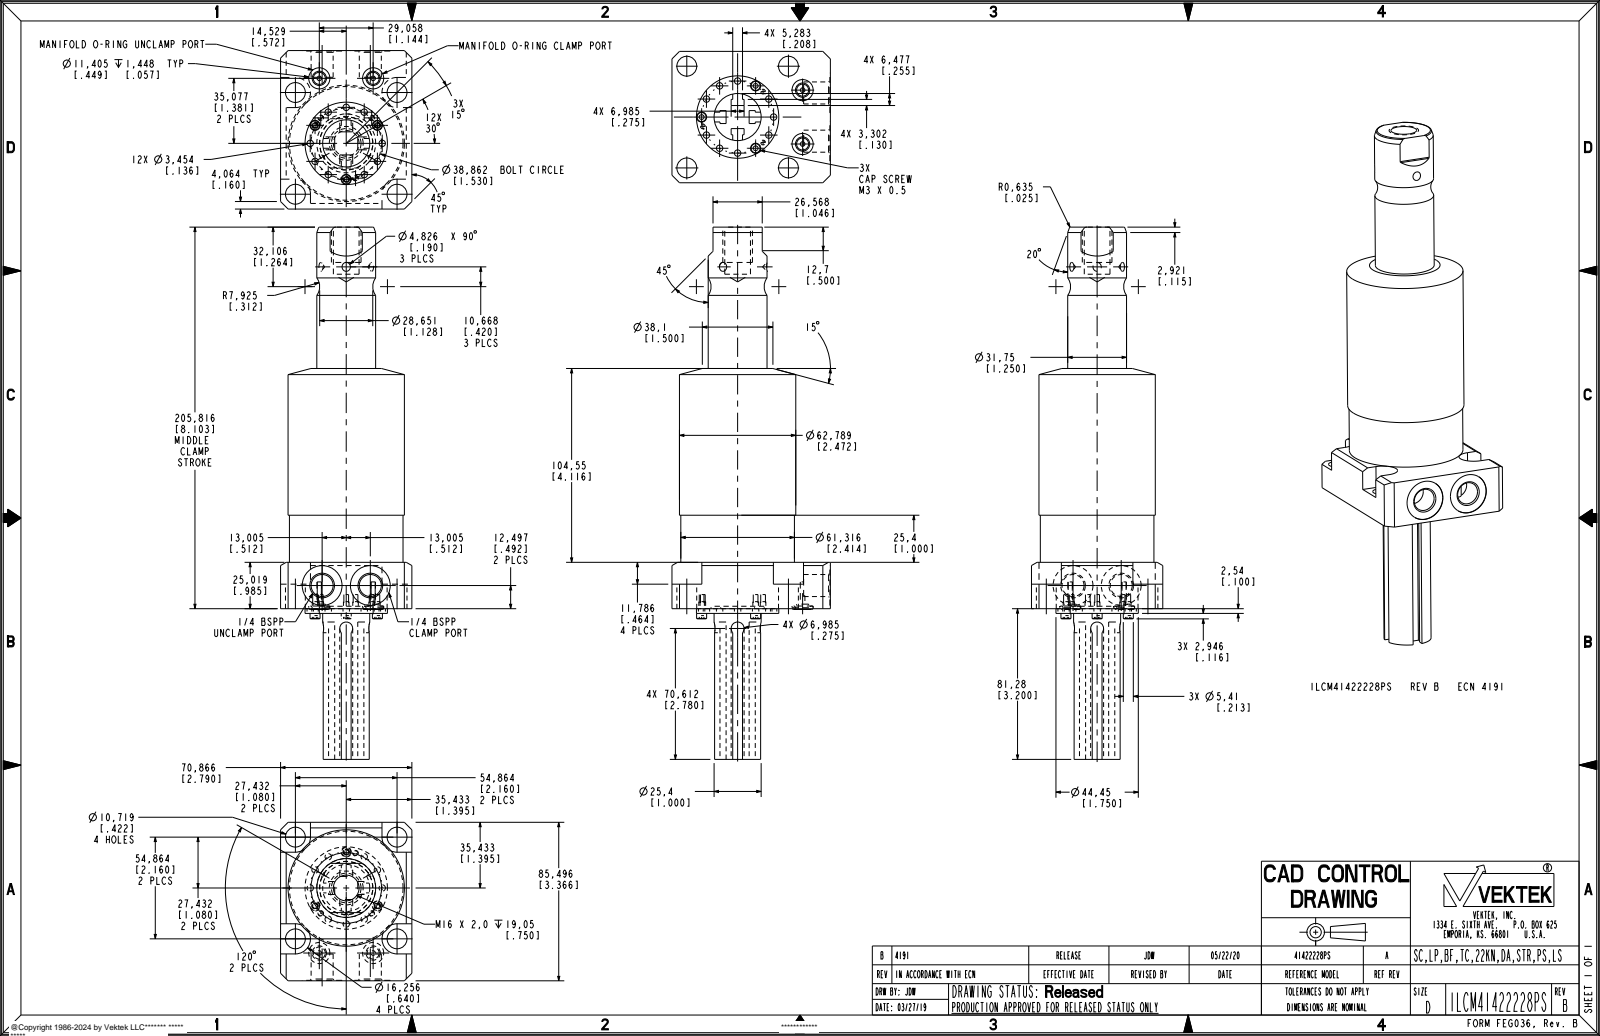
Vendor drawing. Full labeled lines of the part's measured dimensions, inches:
Part name (STEP PRODUCT): ILCM41422228PS
STEP written by: PRO/ENGINEER BY PARAMETRIC TECHNOLOGY CORPORATION, 2013320 (AUTOMOTIVE_DESIGN)
Units: inches
Bodies: 1 solid, 282 faces (134 planar, 114 cylindrical, 34 other)
Overall size (bounding box): 11.303 × 3.366 × 2.79
Volume: 32.53 in³ · Surface area: 102.2 in²
Round holes (diameter × count): ⌀0.136 ×12, ⌀0.1 ×6, ⌀0.422 ×4, ⌀0.098 ×2, ⌀0.256 ×2, ⌀0.449 ×2, ⌀0.468 ×2, ⌀0.846 ×2, ⌀0.546 ×1, ⌀1.13 ×1
Round bosses / shafts (diameter × count): ⌀0.118 ×6, ⌀0.213 ×3, ⌀2.472 ×1, ⌀2.414 ×1, ⌀1.75 ×1, ⌀1.25 ×1, ⌀1 ×1, ⌀0.719 ×1
Partial cylindrical surfaces — rounded edges, fillets, slot ends (radius × count): R0.32 ×4, R0.03 ×2, R0.137 ×2
Main face-to-face distances: 0.107, 0.382, 0.985, 0.141, 0.349, 0.033, 0.241, 1.64, 1.15, 2.79
Hole centre spacings: 0.765, 1.325, 0.396, 0.765, 1.478, 0.813, 1.082, 1.125
